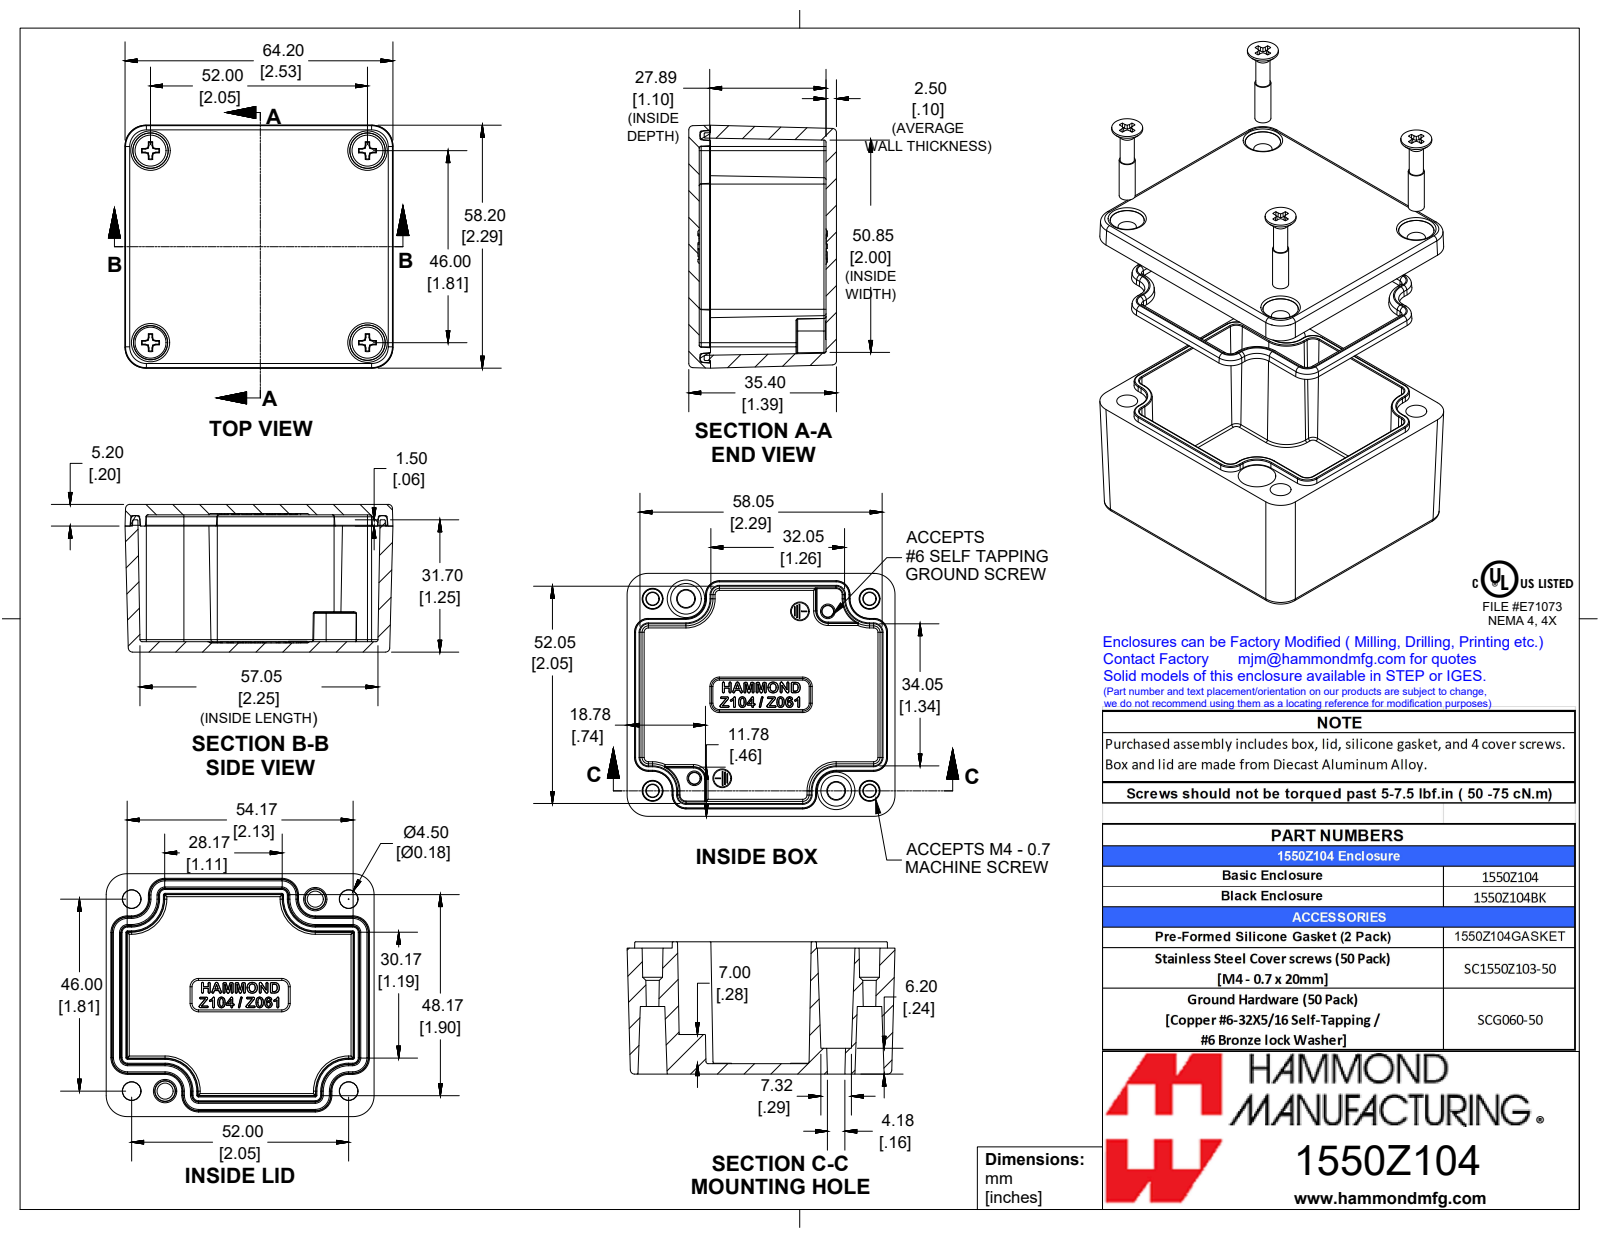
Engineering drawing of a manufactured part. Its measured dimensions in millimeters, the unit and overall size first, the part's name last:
Units: millimetres
Overall size (bounding box): 64.2 × 58.2 × 35.4
Round bosses / shafts (diameter × count): ⌀7.5 ×4, ⌀3.9 ×4, ⌀3.3 ×4
Partial cylindrical surfaces — rounded edges, fillets, slot ends (radius × count): R0.2 ×60, R0.5 ×34, R1 ×28, R0.3 ×20, R5 ×8
Main face-to-face distances: 2.5, 32.9, 35.4, 30.4, 30.2, 2.7, 27.7, 5.2, 9, 27.9
Volume: 48 290 mm³ · Surface area: 37 040 mm²
Bodies: 7 solids, 1398 faces (405 planar, 240 cylindrical, 753 other)
Part name (STEP PRODUCT): 1550Z104
STEP written by: SolidWorks 2019 (AUTOMOTIVE_DESIGN)
